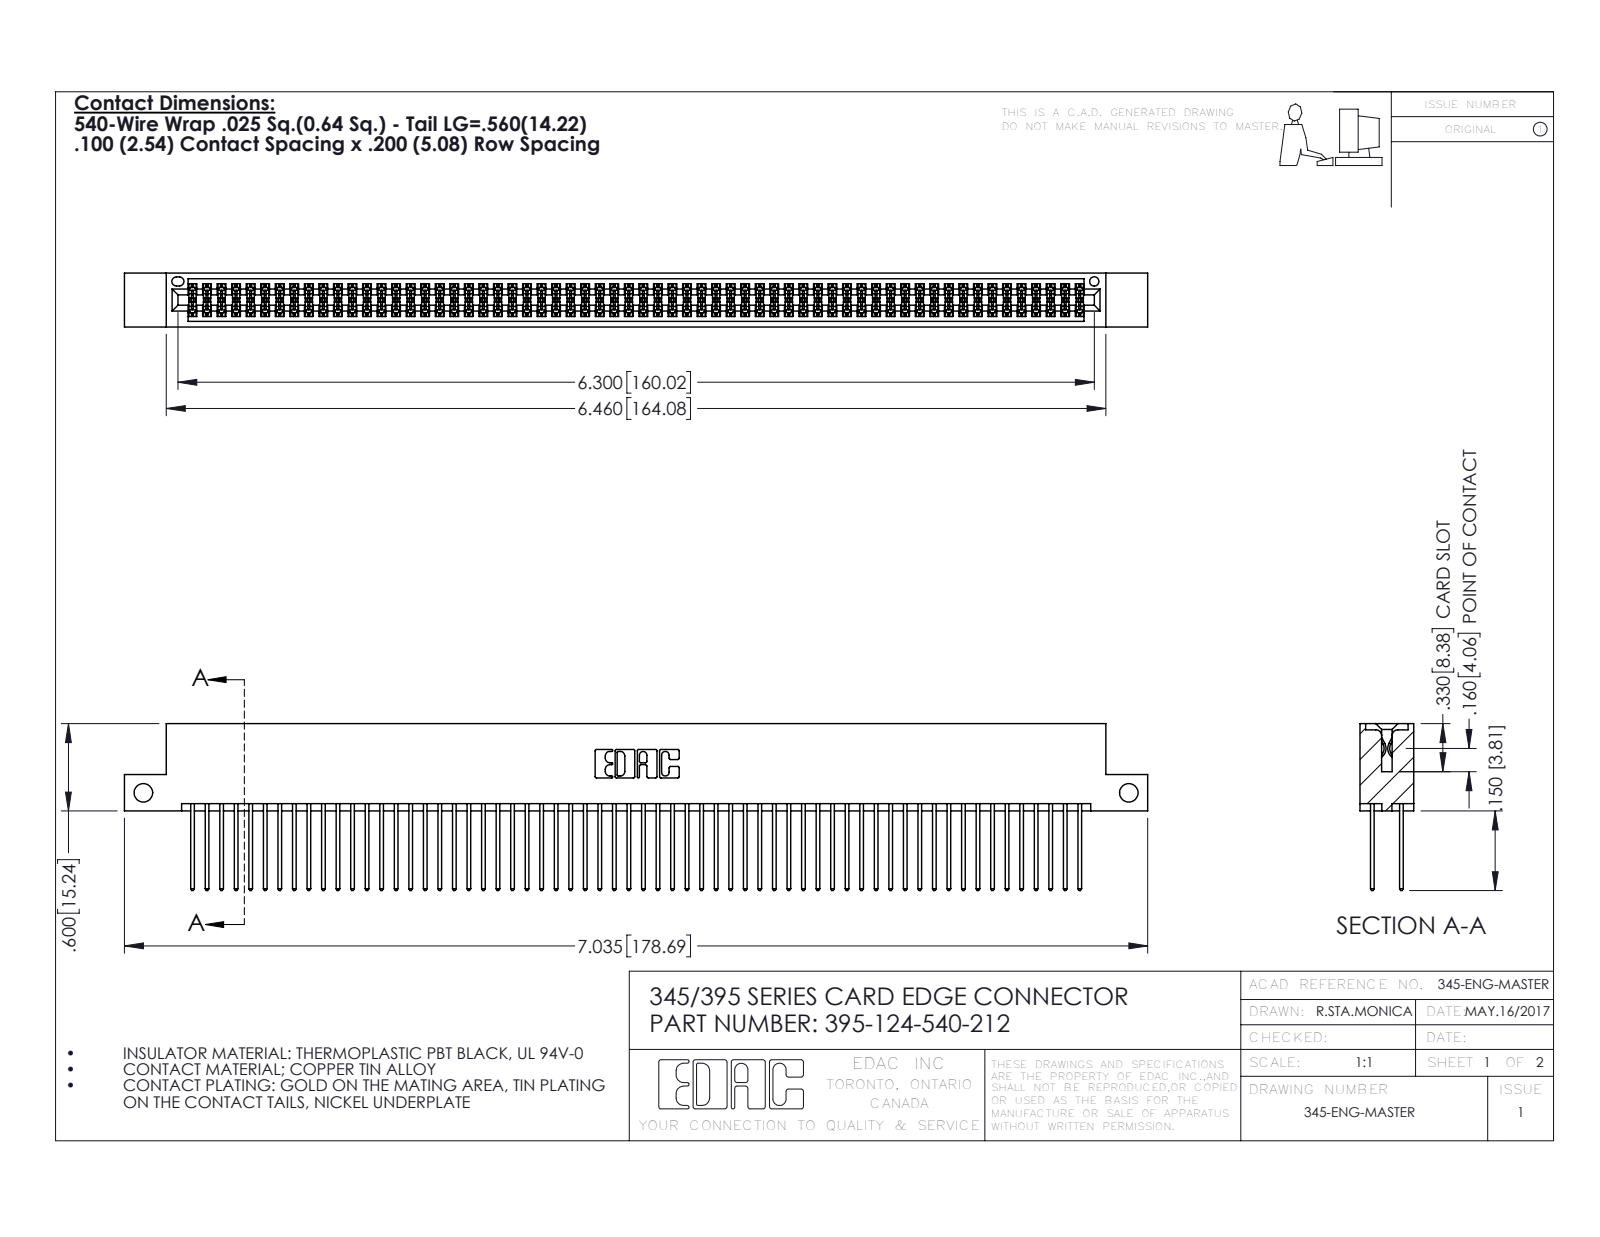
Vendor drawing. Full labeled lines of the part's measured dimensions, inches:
Part name (STEP PRODUCT): 345-292-001_345-293-140; 395-124-540-212; 345 Part_Flush Mounting Lugs - Side Mount
STEP written by: SolidWorks 2016 (CONFIG_CONTROL_DESIGN)
Units: inches
Bodies: 125 solids, 6326 faces (4172 planar, 2154 cylindrical, 0 other)
Overall size (bounding box): 7.035 × 1.147 × 0.37
Volume: 1.094 in³ · Surface area: 44.84 in²
Round holes (diameter × count): ⌀0.128 ×2, ⌀0.064 ×1
Partial cylindrical surfaces — rounded edges, fillets, slot ends (radius × count): R0.006 ×186, R0.01 ×124, R0.01 ×22, R0.007 ×6, R0.031 ×6, R0.026 ×3, R0.014 ×2, R0.019 ×2
Main face-to-face distances: 0.298, 0.072, 0.2, 0.098, 0.272, 0.025, 0.225, 0.37, 0.175, 0.149
Hole centre spacings: 6.775
